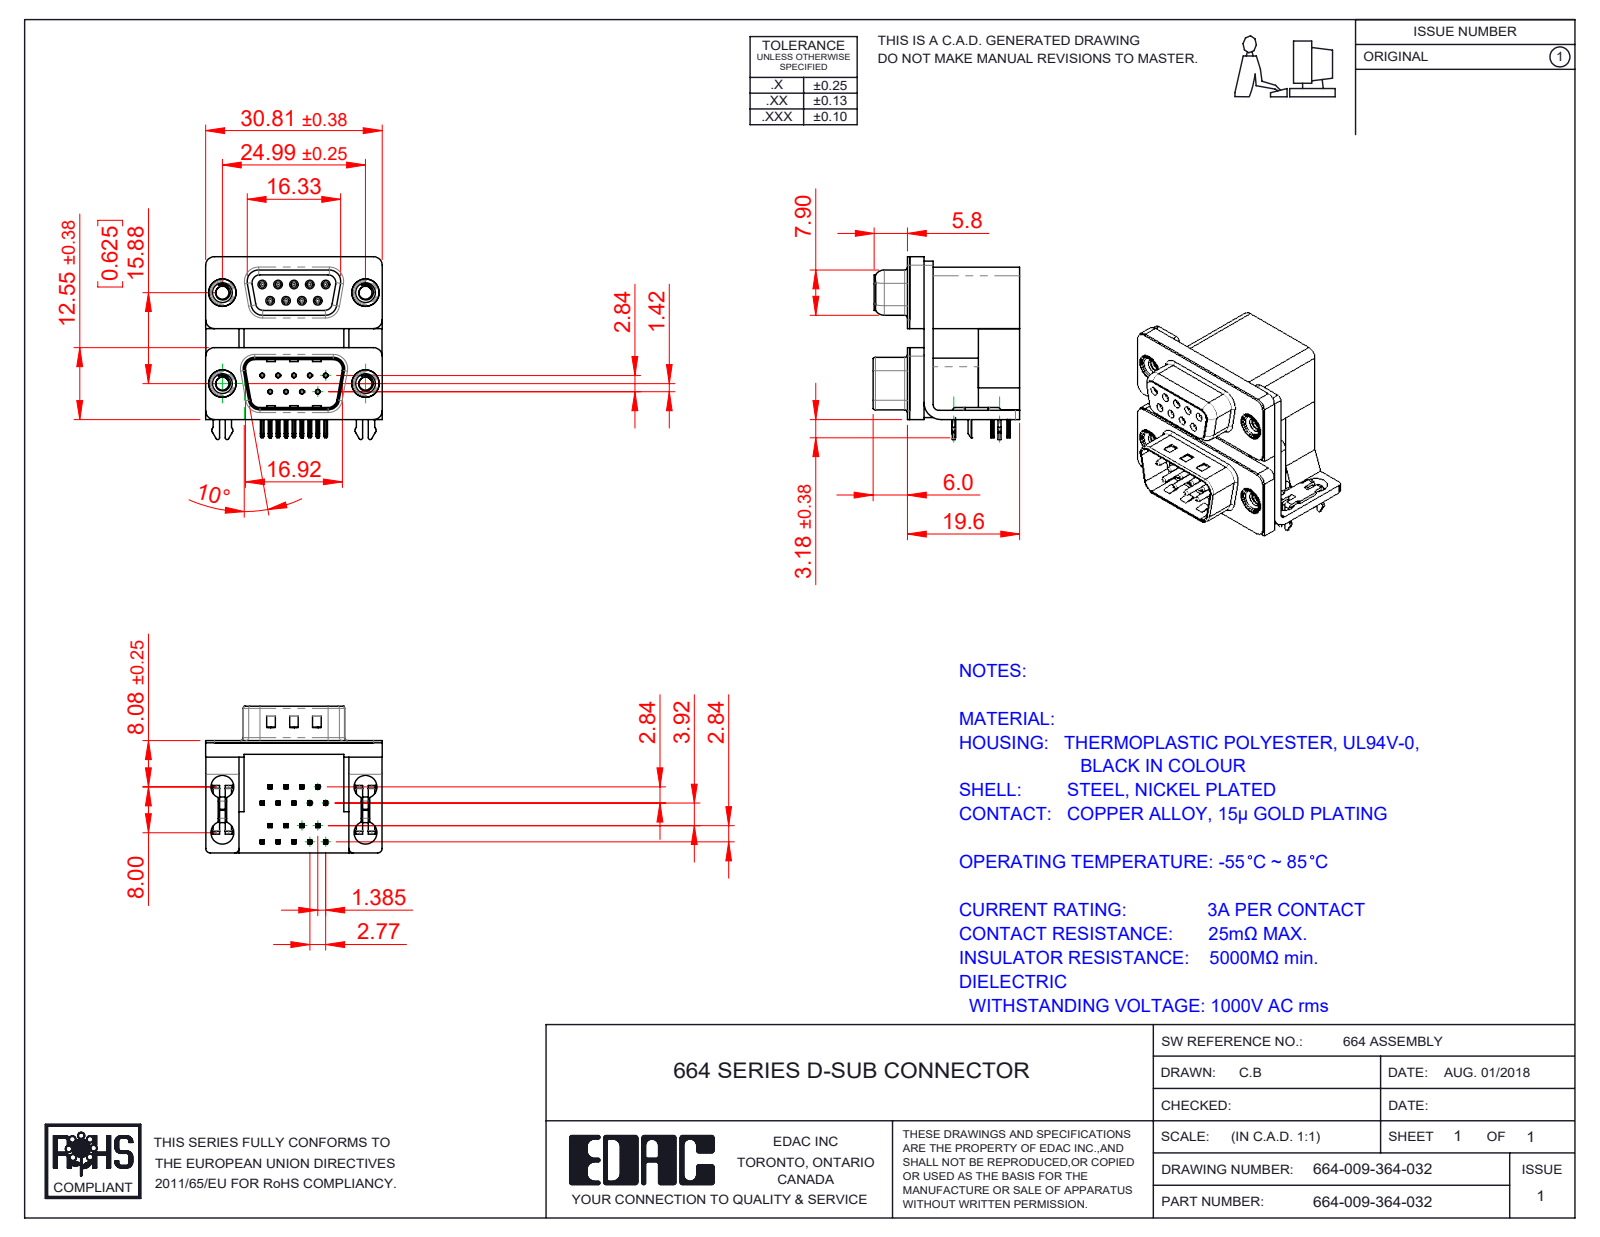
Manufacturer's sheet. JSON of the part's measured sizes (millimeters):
{"part_name": "664 Contact Bottom Upper_L; 664 Contact Top Lower; 664 Contact Bottom Lower; 664 2 Prong Board Lock_3 (+8 more)", "step_written_by": "SolidWorks 2020 (CONFIG_CONTROL_DESIGN)", "units": "millimeters", "bodies": {"solids": 31, "faces": 2681, "planar": 1365, "cylindrical": 745, "other": 571}, "overall_size": [31.93, 30.81, 25.6], "volume_mm3": 10331, "surface_area_mm2": 12376, "round_holes": [[0.8, 18], [0.35, 9], [0.9, 9], [4, 8], [2.26, 4], [3.5, 4], [4.8, 4], [5, 4]], "round_bosses_or_shafts": [[1.2, 9], [0.75, 9], [4.9, 4], [4.75, 4], [3.9, 4]], "partial_cylinders_radius": [[0.1, 74], [0.25, 46], [0.15, 36], [0.12, 18], [0.35, 18], [0.5, 16], [1.5, 13], [0.75, 10]], "face_to_face_distances": [0.4, 2.5, 16.7, 19.2, 19.6, 2.9, 7.2, 9.5, 12, 12.4], "hole_center_spacings": [3.16, 2.77, 16.12, 15.88, 5.54, 16.82, 13.11, 18.77]}
